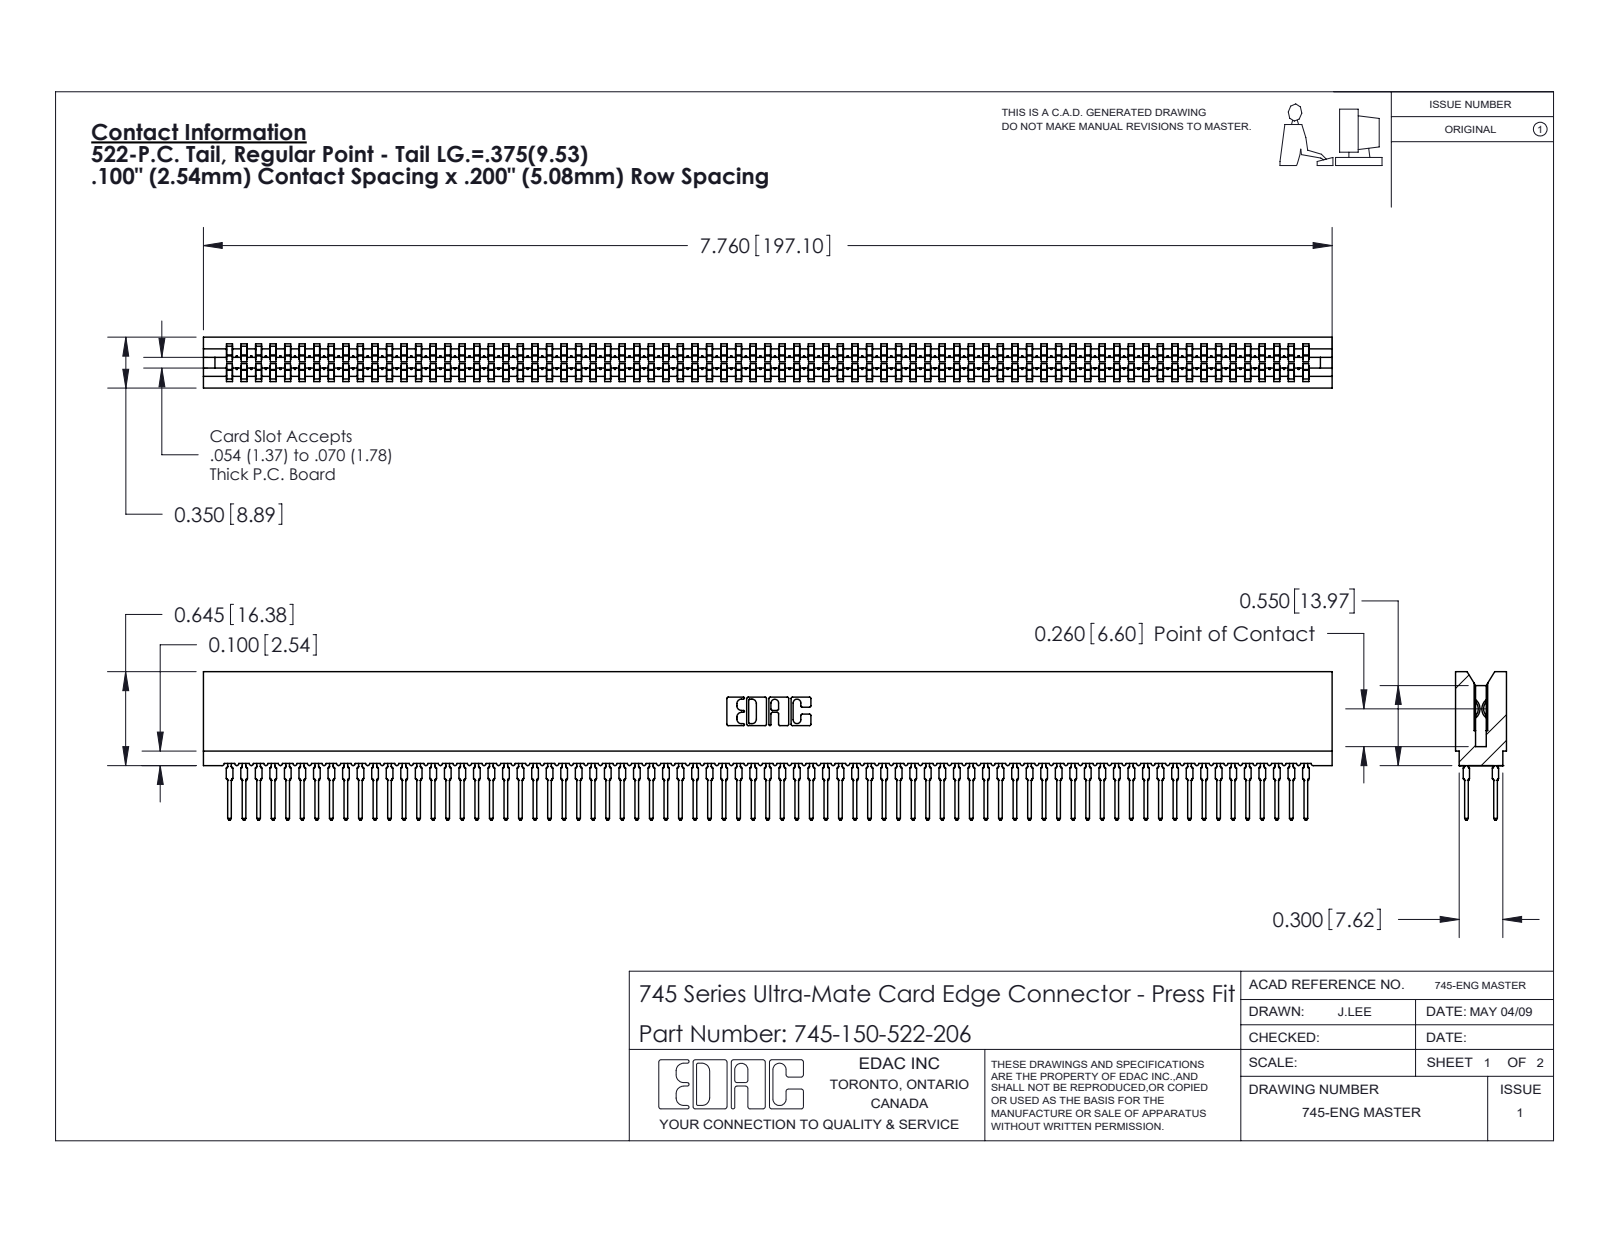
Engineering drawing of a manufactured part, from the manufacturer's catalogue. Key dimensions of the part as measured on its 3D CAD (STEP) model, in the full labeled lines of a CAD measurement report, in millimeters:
Part name (STEP PRODUCT): 745-150-522-206; 745-292-001_522; 745 Part_Insulator Option - 06
STEP written by: SolidWorks 2020 (CONFIG_CONTROL_DESIGN)
Units: millimetres
Bodies: 151 solids, 13521 faces (6956 planar, 2665 cylindrical, 3900 other)
Overall size (bounding box): 197.1 × 25.9 × 8.9
Volume: 17 680 mm³ · Surface area: 37 270 mm²
Partial cylindrical surfaces — rounded edges, fillets, slot ends (radius × count): R0.5 ×300, R0.4 ×150, R0.3 ×22, R0.1 ×8, R0.3 ×8, R0.2 ×6, R0.8 ×6, R0.7 ×3
Main face-to-face distances: 8.9, 1.6, 7.3, 1.1, 7.7, 0.5, 6.2, 3.5, 5.4, 2.4
